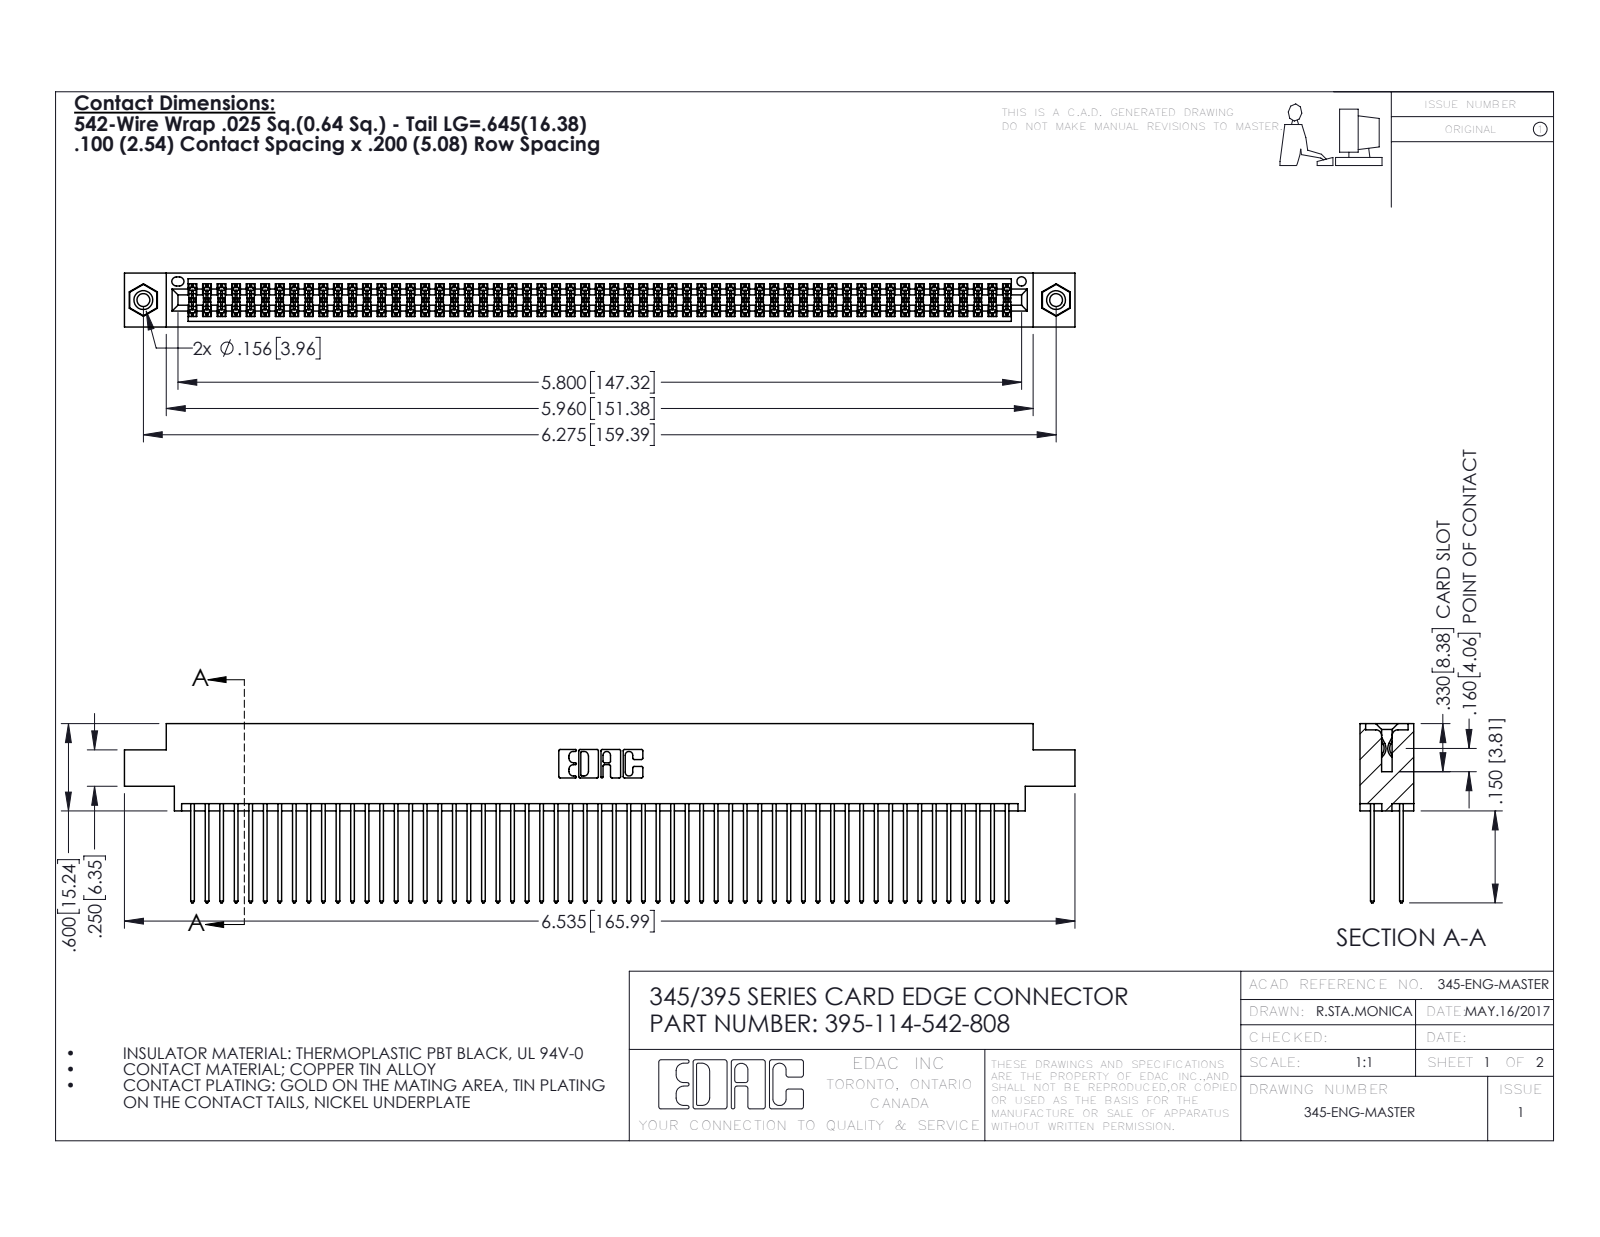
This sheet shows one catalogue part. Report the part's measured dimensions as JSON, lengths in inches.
{"part_name": "345-292-001_345-293-142; 345 Part_0.170 Offset - 0.156 Dia-TI; 345-250-001_345-250-003-102; 395-114-542-808", "step_written_by": "SolidWorks 2016 (CONFIG_CONTROL_DESIGN)", "units": "inches", "bodies": {"solids": 117, "faces": 5890, "planar": 3878, "cylindrical": 1996, "other": 16}, "overall_size": [6.535, 1.232, 0.37], "volume_in3": 1.018, "surface_area_in2": 42.75, "round_holes": [[0.089, 2], [0.125, 2], [0.156, 2], [0.064, 1]], "round_bosses_or_shafts": [[0.155, 2]], "partial_cylinders_radius": [[0.006, 171], [0.01, 114], [0.01, 22], [0.007, 6], [0.031, 6], [0.026, 3], [0.014, 2], [0.019, 2]], "face_to_face_distances": [0.072, 0.298, 0.2, 0.098, 0.272, 0.025, 0.37, 0.225, 0.175, 0.149], "hole_center_spacings": [0.27, 6.039, 6.275]}
